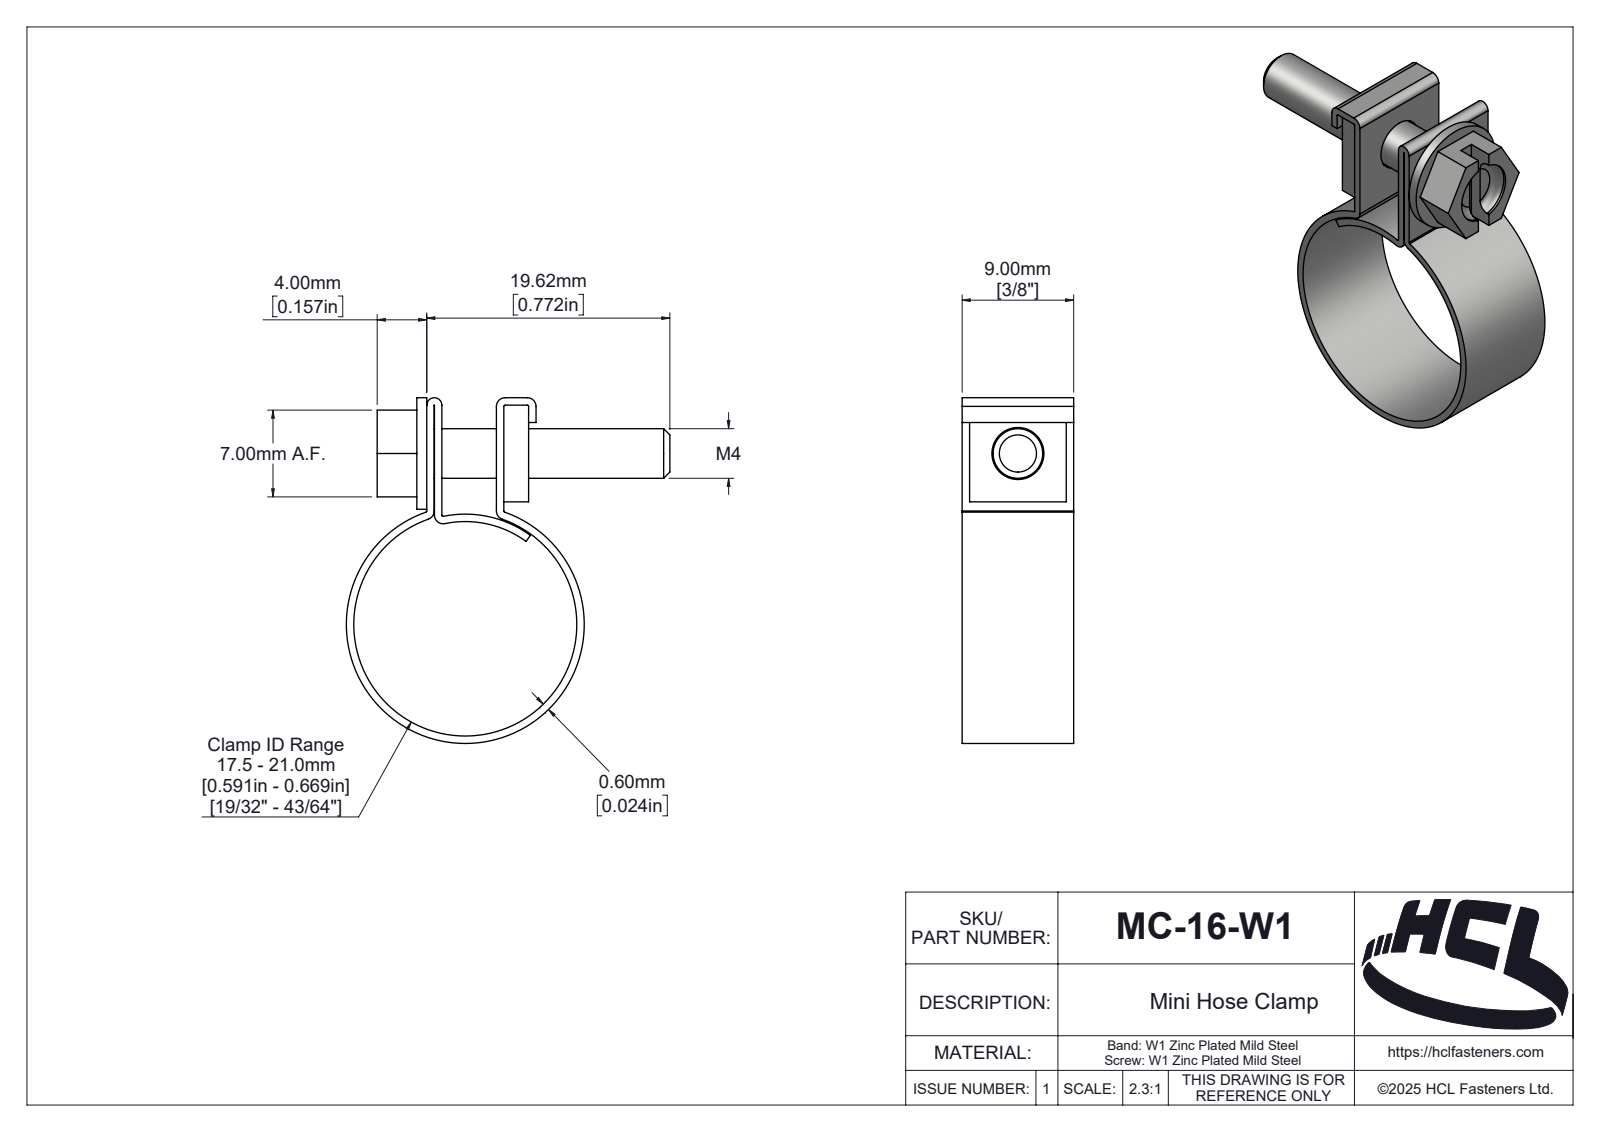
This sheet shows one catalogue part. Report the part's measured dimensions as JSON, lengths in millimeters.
{"part_name": "MC-16-W1", "step_written_by": "SolidWorks 2025 (AUTOMOTIVE_DESIGN)", "units": "millimeters", "bodies": {"solids": 3, "faces": 175, "planar": 38, "cylindrical": 84, "other": 53}, "overall_size": [27.89, 26.11, 9], "volume_mm3": 969, "surface_area_mm2": 2400, "round_holes": [[4.2, 1], [5, 1], [18, 1]], "round_bosses_or_shafts": [[19.2, 1], [9, 1], [4, 1]], "partial_cylinders_radius": [[0.1, 5], [0.7, 5], [0.2, 1], [0.61, 1], [0.81, 1], [1.01, 1], [1.06, 1], [1.28, 1]], "face_to_face_distances": [0.6, 0.62, 5, 5.62, 6.22, 7, 2, 2.6, 8.22, 7.6]}
